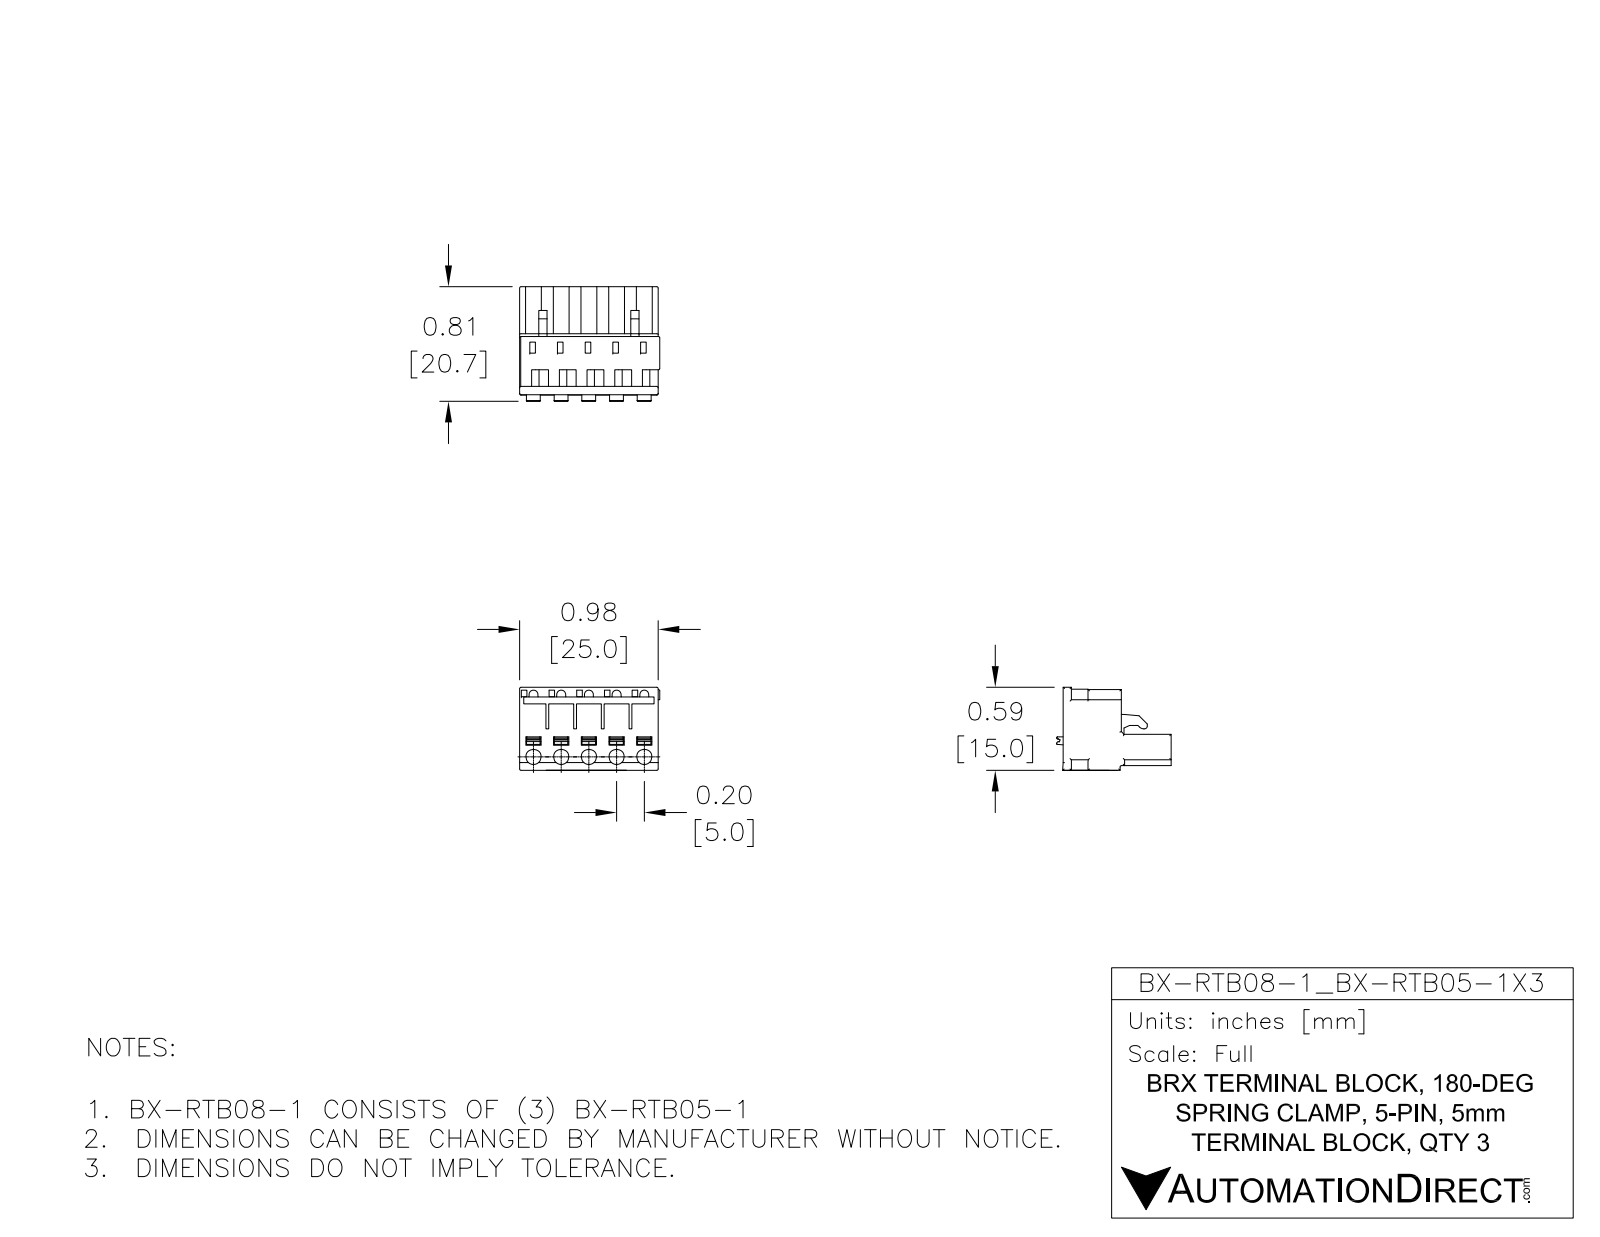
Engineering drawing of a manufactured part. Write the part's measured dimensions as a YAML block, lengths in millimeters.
part_name: "BX-RTB08-1"
step_written_by: "SolidWorks 2017 (AUTOMOTIVE_DESIGN)"
units: millimeters
bodies: {solids: 3, faces: 1962, planar: 1014, cylindrical: 612, other: 336}
overall_size: [100.7, 20.7, 15]
volume: 13400
surface_area: 10360
round_holes:
  - {diameter: 1.6, count: 15}
  - {diameter: 2.7, count: 15}
  - {diameter: 3.1, count: 15}
partial_cylinders:
  - {radius: 0.1, count: 180}
  - {radius: 0.3, count: 108}
  - {radius: 0.8, count: 15}
  - {radius: 1, count: 15}
  - {radius: 2.4, count: 15}
  - {radius: 2.5, count: 15}
  - {radius: 0.2, count: 4}
  - {radius: 0.3, count: 1}
face_to_face_distances: [37.7, 14.6, 25, 5.7, 8.9, 10.5, 9, 75.4, 1.5, 62.7]
hole_center_spacings: [5, 5.1, 37.7, 37.7, 10, 10.1, 32.7, 32.7]
